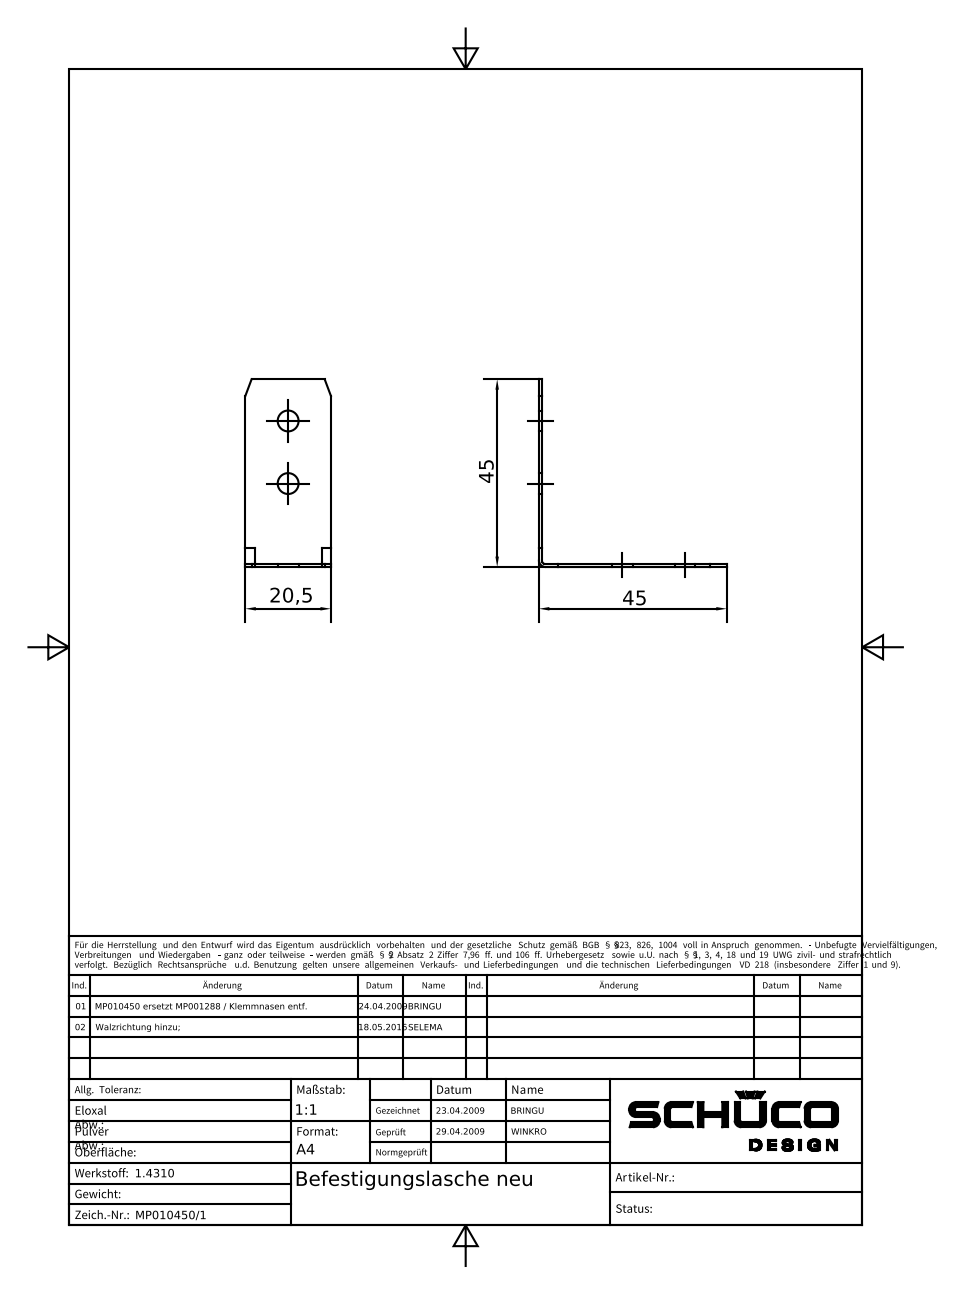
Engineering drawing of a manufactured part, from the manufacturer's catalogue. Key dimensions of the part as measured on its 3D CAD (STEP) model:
Part name (STEP PRODUCT): MP010450
STEP written by: Autodesk Inventor 2024 (AUTOMOTIVE_DESIGN)
Units: millimetres
Bodies: 1 solid, 26 faces (20 planar, 6 cylindrical, 0 other)
Overall size (bounding box): 45 × 45 × 20.5
Volume: 1 353 mm³ · Surface area: 3 616 mm²
Round holes (diameter × count): ⌀5 ×4
Partial cylindrical surfaces — rounded edges, fillets, slot ends (radius × count): R0.5 ×1, R1.6 ×1
Main face-to-face distances: 0.8, 20.5, 45, 44.2, 2.25, 18.25, 4.5, 3.7, 40.5, 16
Hole centre spacings: 15
